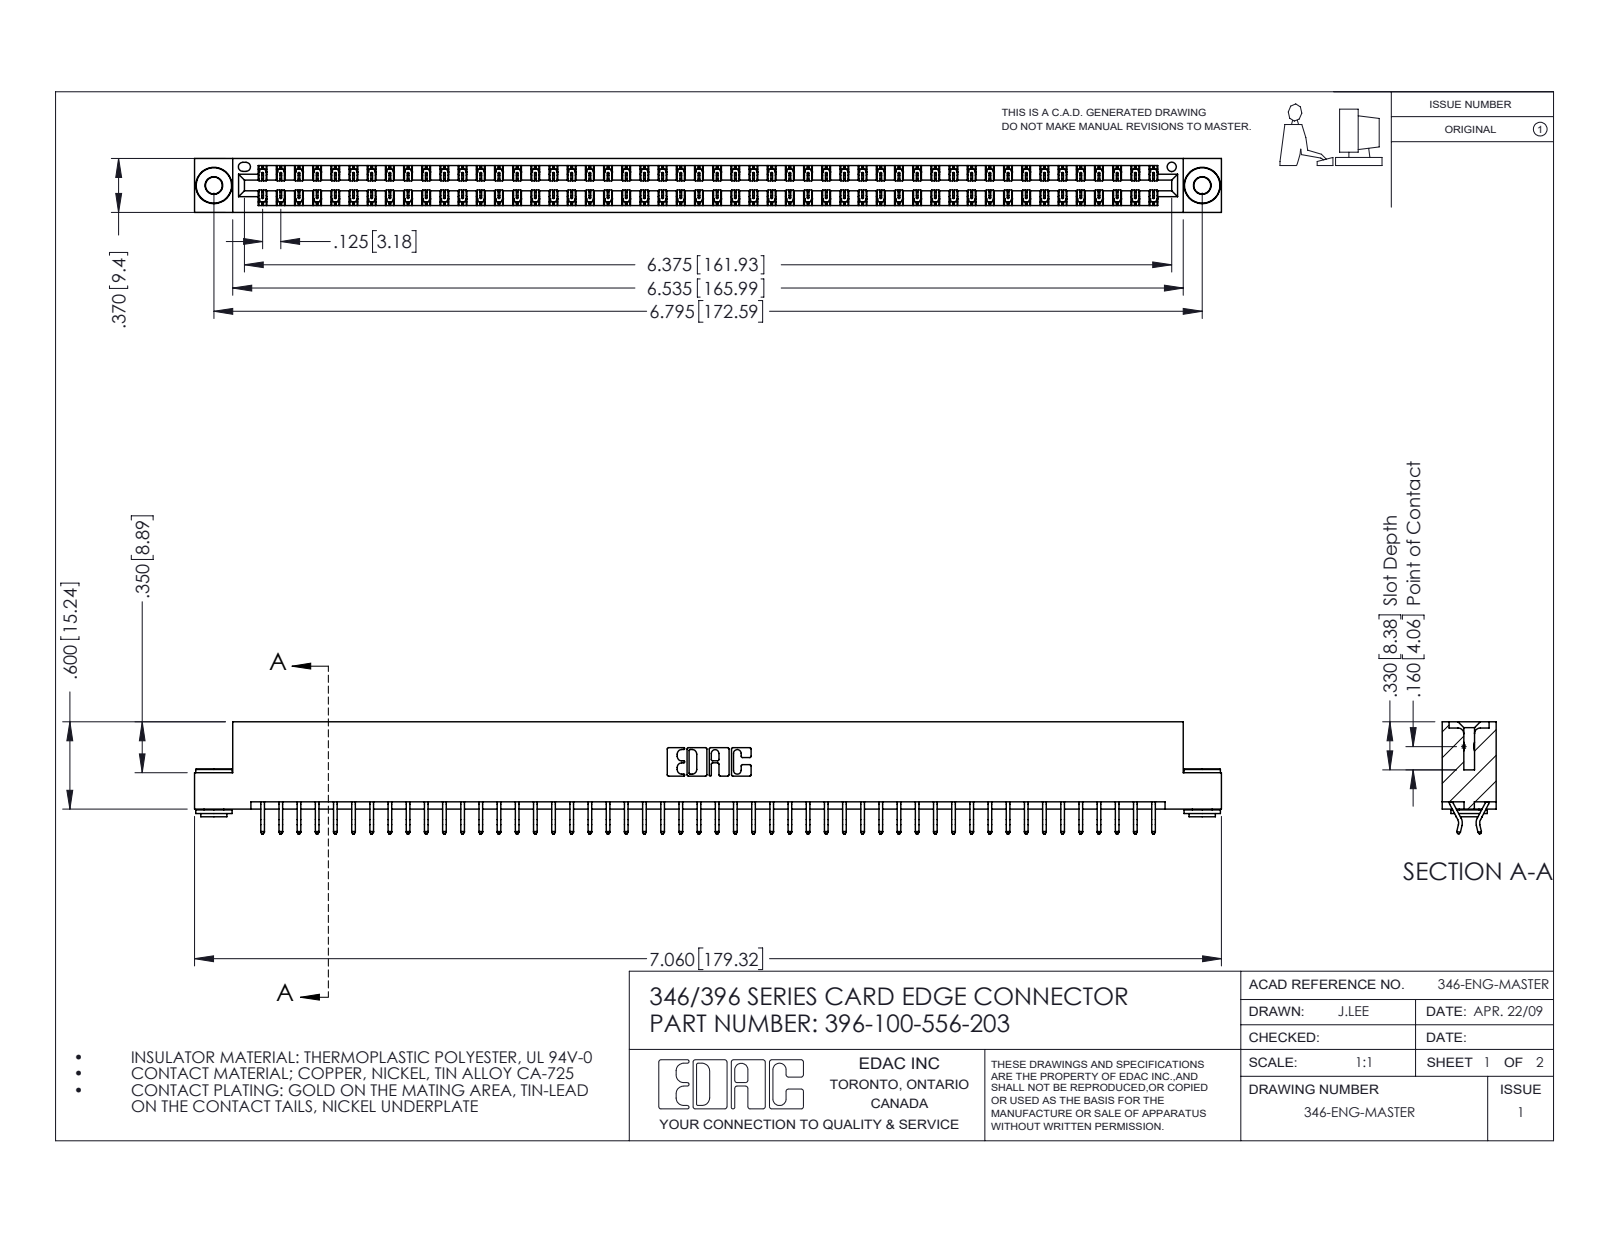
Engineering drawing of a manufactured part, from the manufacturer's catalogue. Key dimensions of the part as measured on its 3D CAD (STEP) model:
Part name (STEP PRODUCT): 346 Part_Flush Mounting Lugs - 0.156 Dia-TH; 396-100-556-203; 345-250-002_345-250-002-102; 345-292-001_556 Tail
STEP written by: SolidWorks 2016 (CONFIG_CONTROL_DESIGN)
Units: inches
Bodies: 103 solids, 5960 faces (3986 planar, 1966 cylindrical, 8 other)
Overall size (bounding box): 7.06 × 0.77 × 0.37
Volume: 1.072 in³ · Surface area: 37.8 in²
Round holes (diameter × count): ⌀0.116 ×2, ⌀0.156 ×2, ⌀0.064 ×1
Round bosses / shafts (diameter × count): ⌀0.25 ×2, ⌀0.18 ×2, ⌀0.136 ×2
Partial cylindrical surfaces — rounded edges, fillets, slot ends (radius × count): R0.006 ×150, R0.01 ×22, R0.007 ×6, R0.031 ×6, R0.026 ×3, R0.01 ×2, R0.014 ×2, R0.022 ×2
Main face-to-face distances: 0.048, 0.322, 0.37, 0.25, 0.025, 0.072, 0.298, 0.275, 0.148, 0.222
Hole centre spacings: 0.246, 6.586, 6.795
